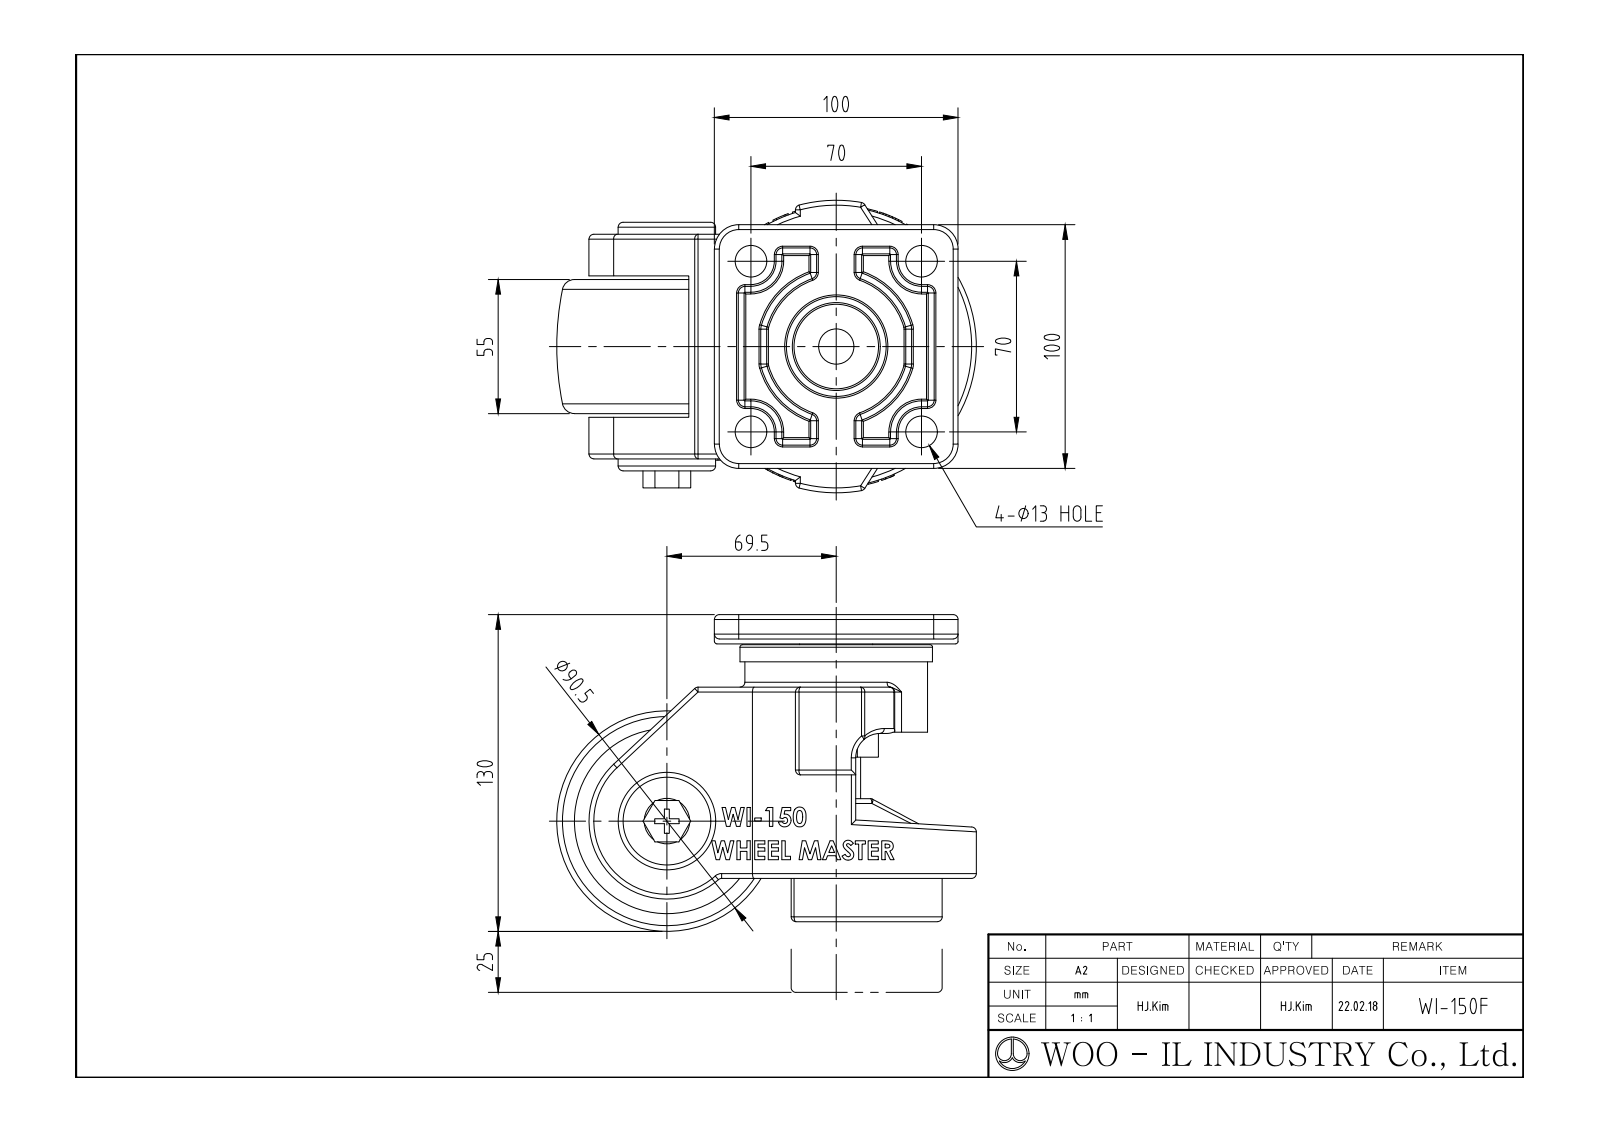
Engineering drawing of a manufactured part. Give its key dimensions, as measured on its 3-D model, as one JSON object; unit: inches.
{"part_name": "WI-150F", "step_written_by": "SolidWorks 2019 (AUTOMOTIVE_DESIGN)", "units": "inches", "bodies": {"solids": 1, "faces": 1013, "planar": 323, "cylindrical": 281, "other": 409}, "overall_size": [6.772, 5.177, 5.118], "volume_in3": 68.96, "surface_area_in2": 251.9, "round_holes": [[0.512, 4], [0.27, 1], [0.335, 1], [0.571, 1], [0.732, 1], [1.291, 1], [2.114, 1], [2.492, 1], [2.52, 1], [2.949, 1]], "round_bosses_or_shafts": [[0.787, 2], [3.075, 1], [2.933, 1], [2.733, 1], [1.575, 1], [1.142, 1], [0.925, 1], [0.334, 1]], "partial_cylinders_radius": [[0.039, 50], [0.079, 46], [0.197, 30], [0.118, 7], [0.394, 4], [0.591, 1], [1.26, 1], [1.732, 1]], "face_to_face_distances": [0.059, 2.224, 0.079, 0.709, 0.669, 0.728, 2.894, 2.953, 0.472, 2.165], "hole_center_spacings": [1.949, 2.756, 3.897, 3.818]}
